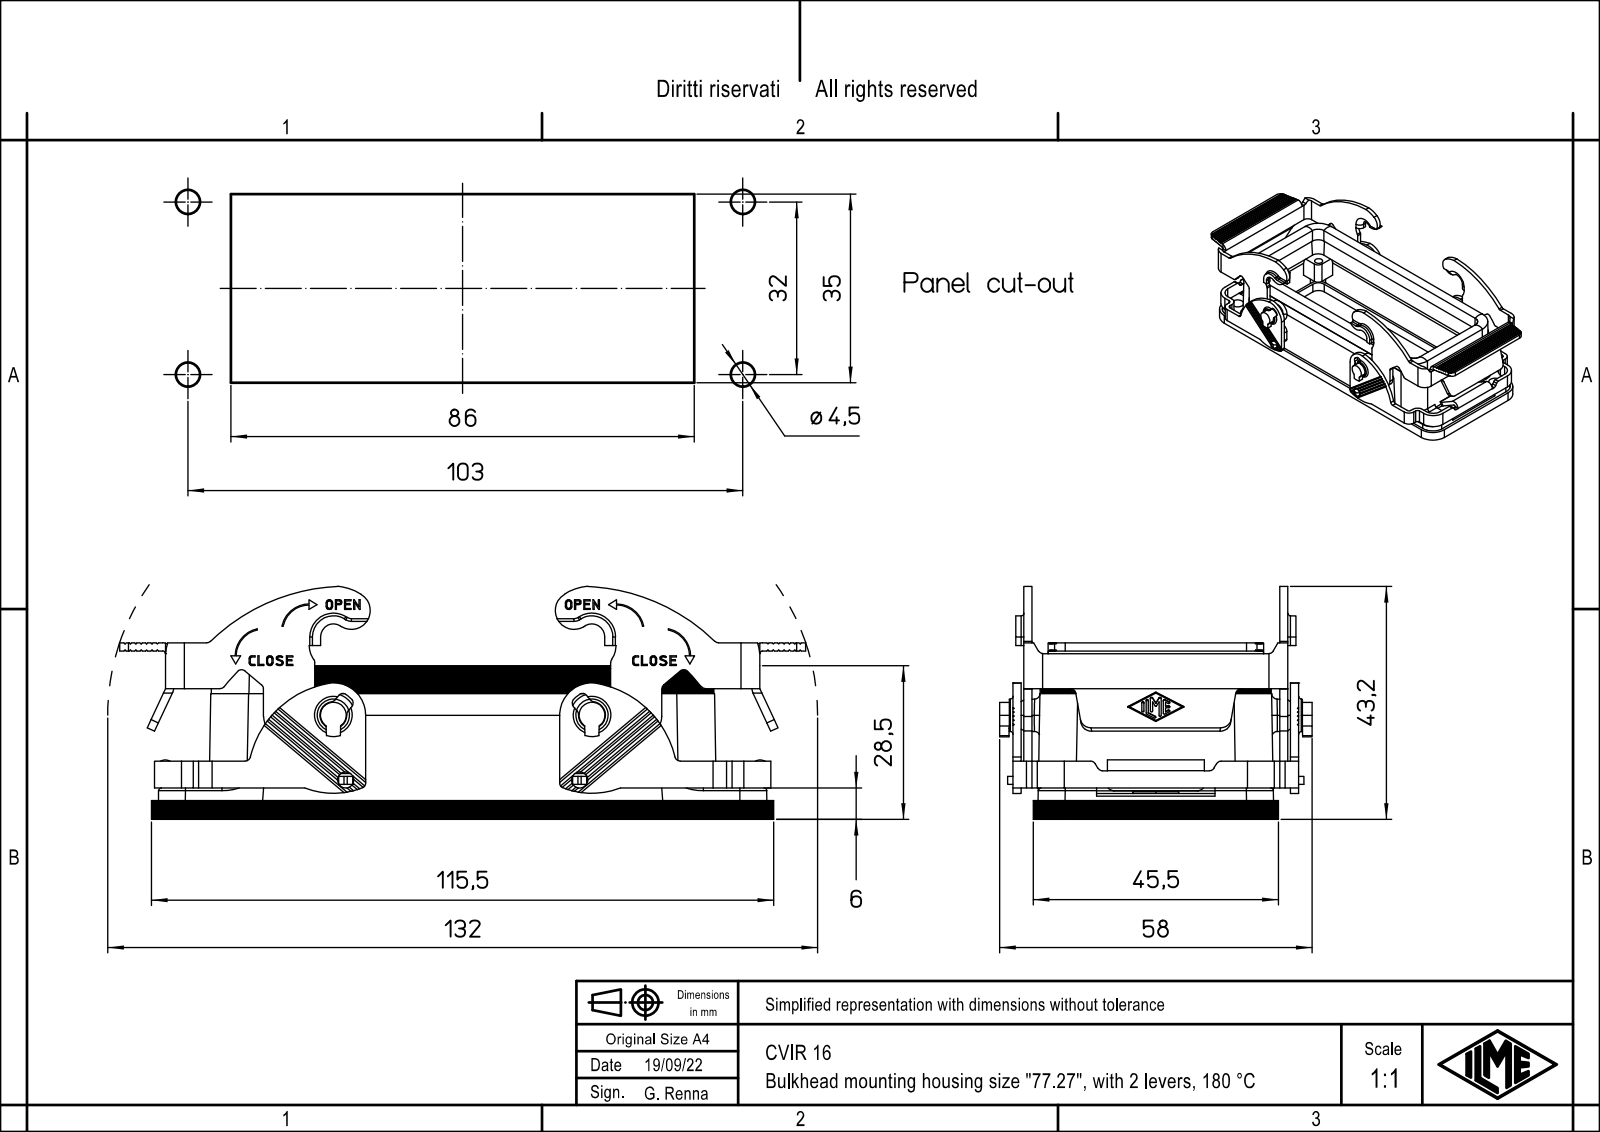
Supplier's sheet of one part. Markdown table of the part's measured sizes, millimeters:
| quantity | value |
| --- | --- |
| part name | CVIR 16 |
| STEP written by | Creo Elements/Direct Modeling 20.1B 02-Apr-2019 (C) Parametric Technology GmbH (AUTOMOTIVE_DESIGN) |
| units | millimeters |
| bodies | 1 solid, 1068 faces (603 planar, 361 cylindrical, 104 other) |
| overall size | 127.33 × 58 × 43.2 |
| volume | 41 494 mm³ |
| surface area | 40 971 mm² |
| round holes (diameter × count) | 3 × 6, 3.8 × 4, 6.2 × 2 |
| round bosses / shafts (diameter × count) | 6 × 2, 4.8 × 2 |
| partial cylindrical surfaces (radius × count) | 1 × 54, 2 × 36, 0.5 × 24, 4 × 14, 3.5 × 12, 5 × 12, 0.17 × 11, 2.5 × 10 |
| main face-to-face distances | 1.5, 2, 49.5, 47.5, 3.5, 0.5, 48, 51, 51.5, 3 |
| hole center spacings | 13.24, 32.24, 90.03, 94.71, 12.22, 27, 32, 47.25 |
